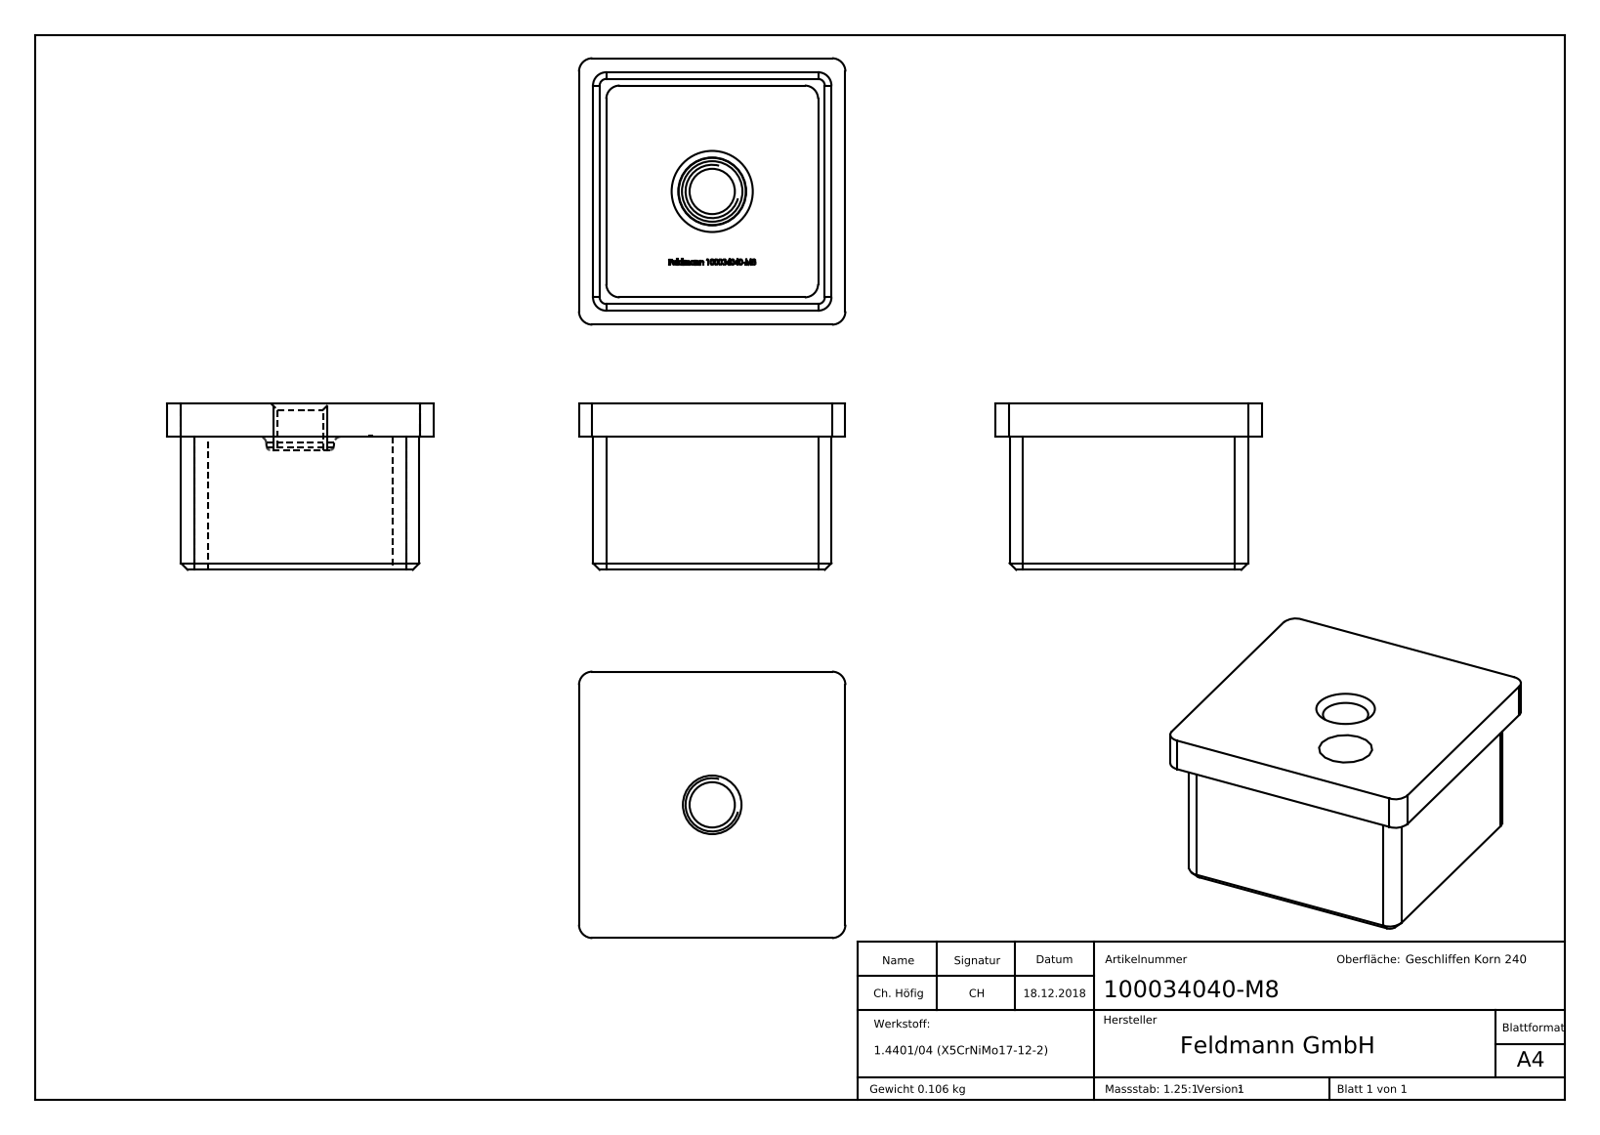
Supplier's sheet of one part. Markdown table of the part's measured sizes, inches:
| quantity | value |
| --- | --- |
| part name | 100034040-M8 |
| STEP written by | SolidWorks 2015 (CONFIG_CONTROL_DESIGN) |
| units | inches |
| bodies | 1 solid, 309 faces (159 planar, 14 cylindrical, 136 other) |
| overall size | 1.575 × 1.575 × 0.984 |
| volume | 0.807 in³ |
| surface area | 14.38 in² |
| round holes (diameter × count) | 0.268 × 1 |
| partial cylindrical surfaces (radius × count) | 0.079 × 12 |
| main face-to-face distances | 0.079, 1.331, 1.409, 0.197, 1.252, 0.083, 0.161, 1.413, 1.492, 1.575 |
